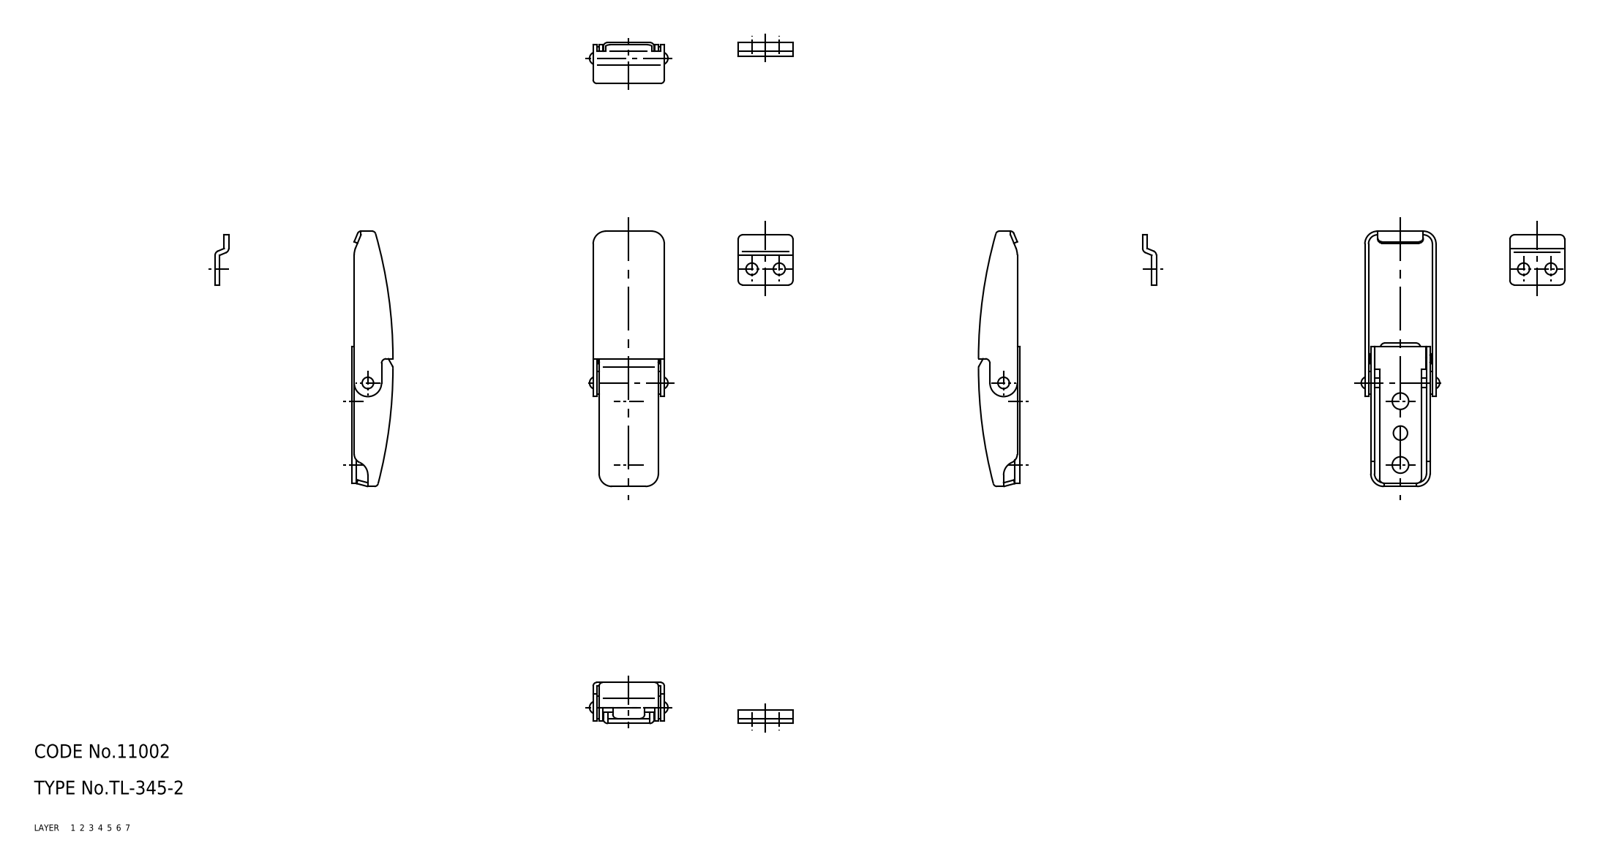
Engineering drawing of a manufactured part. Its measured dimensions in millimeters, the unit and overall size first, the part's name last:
Units: millimetres
Overall size (bounding box): 56 × 17.2 × 9
Volume: 2 004 mm³ · Surface area: 5 418 mm²
Bodies: 10 solids, 212 faces (0 planar, 0 cylindrical, 212 other)
Part name (STEP PRODUCT): washer; shaft_B; shaft_A; rivet (+6 more)
STEP written by: CADfix (AUTOMOTIVE_DESIGN)
